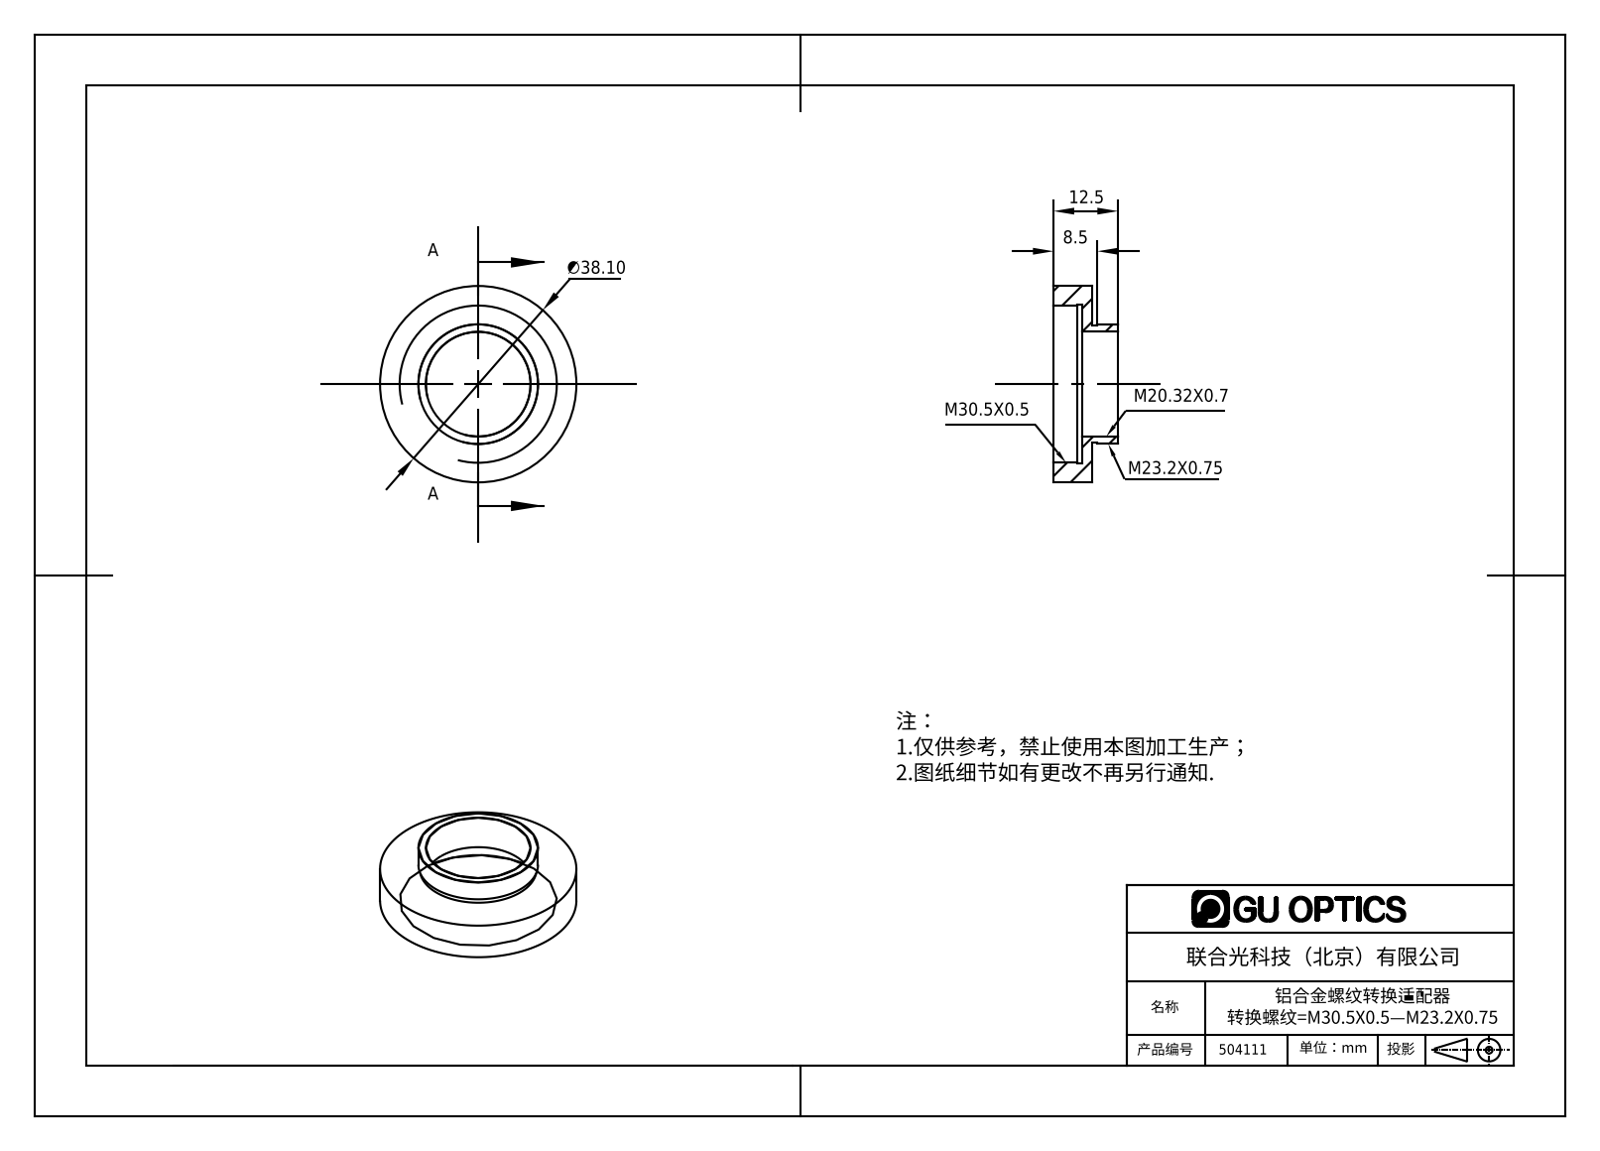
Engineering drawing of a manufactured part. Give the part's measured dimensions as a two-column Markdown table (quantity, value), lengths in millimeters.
| quantity | value |
| --- | --- |
| part name | 504111 |
| STEP written by | SolidWorks 2016 (AUTOMOTIVE_DESIGN) |
| units | millimeters |
| bodies | 1 solid, 18 faces (6 planar, 12 cylindrical, 0 other) |
| overall size | 38.1 × 38.1 × 12.5 |
| volume | 4 360 mm³ |
| surface area | 3 926 mm² |
| round holes (diameter × count) | 20.3 × 1, 30.48 × 1, 30.7 × 1 |
| round bosses / shafts (diameter × count) | 38.1 × 1, 23.22 × 1, 22.7 × 1 |
| main face-to-face distances | 2, 5.5, 7.5, 12.5, 7, 5, 1, 3, 4, 8.5 |
